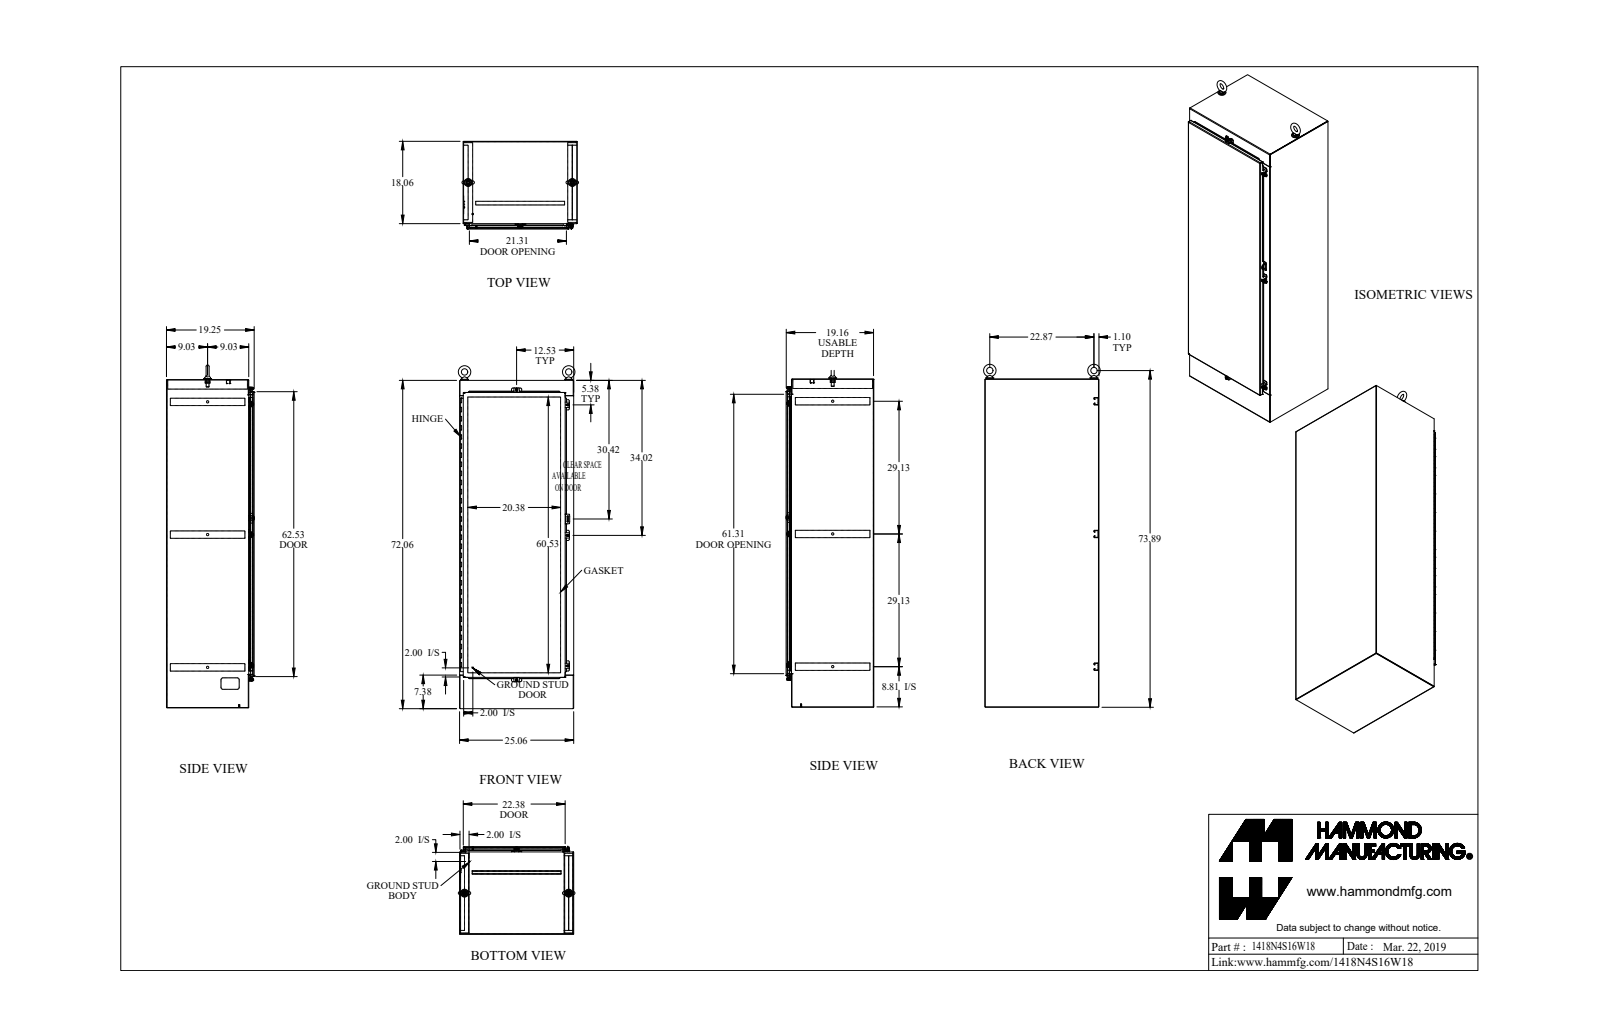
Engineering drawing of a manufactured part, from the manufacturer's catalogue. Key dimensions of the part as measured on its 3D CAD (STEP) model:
Part name (STEP PRODUCT): 1418N4S16W18_Default
STEP written by: SolidWorks 2019 (CONFIG_CONTROL_DESIGN)
Units: inches
Bodies: 56 solids, 1938 faces (954 planar, 844 cylindrical, 140 other)
Overall size (bounding box): 75.719 × 26.118 × 19.31
Volume: 821.8 in³ · Surface area: 17 465 in²
Round holes (diameter × count): ⌀0.304 ×10, ⌀0.213 ×5, ⌀0.265 ×5, ⌀0.375 ×5, ⌀0.5 ×3, ⌀0.527 ×2, ⌀0.625 ×2, ⌀0.68 ×2, ⌀0.75 ×2, ⌀0.11 ×1, ⌀0.125 ×1
Round bosses / shafts (diameter × count): ⌀0.5 ×5, ⌀0.39 ×5, ⌀0.244 ×5, ⌀1.75 ×2, ⌀1.5 ×2, ⌀1.25 ×2, ⌀0.738 ×2, ⌀0.313 ×2
Partial cylindrical surfaces — rounded edges, fillets, slot ends (radius × count): R0.043 ×60, R0.138 ×54, R0.048 ×43, R0.143 ×43, R0.25 ×26, R0.06 ×10, R0.141 ×10, R0.125 ×8
Main face-to-face distances: 0.095, 19.152, 24.965, 24.87, 19.057, 19.247, 25.06, 1.187, 17.965, 71.965
Hole centre spacings: 6, 12, 18, 24, 30, 36, 42, 29.13
